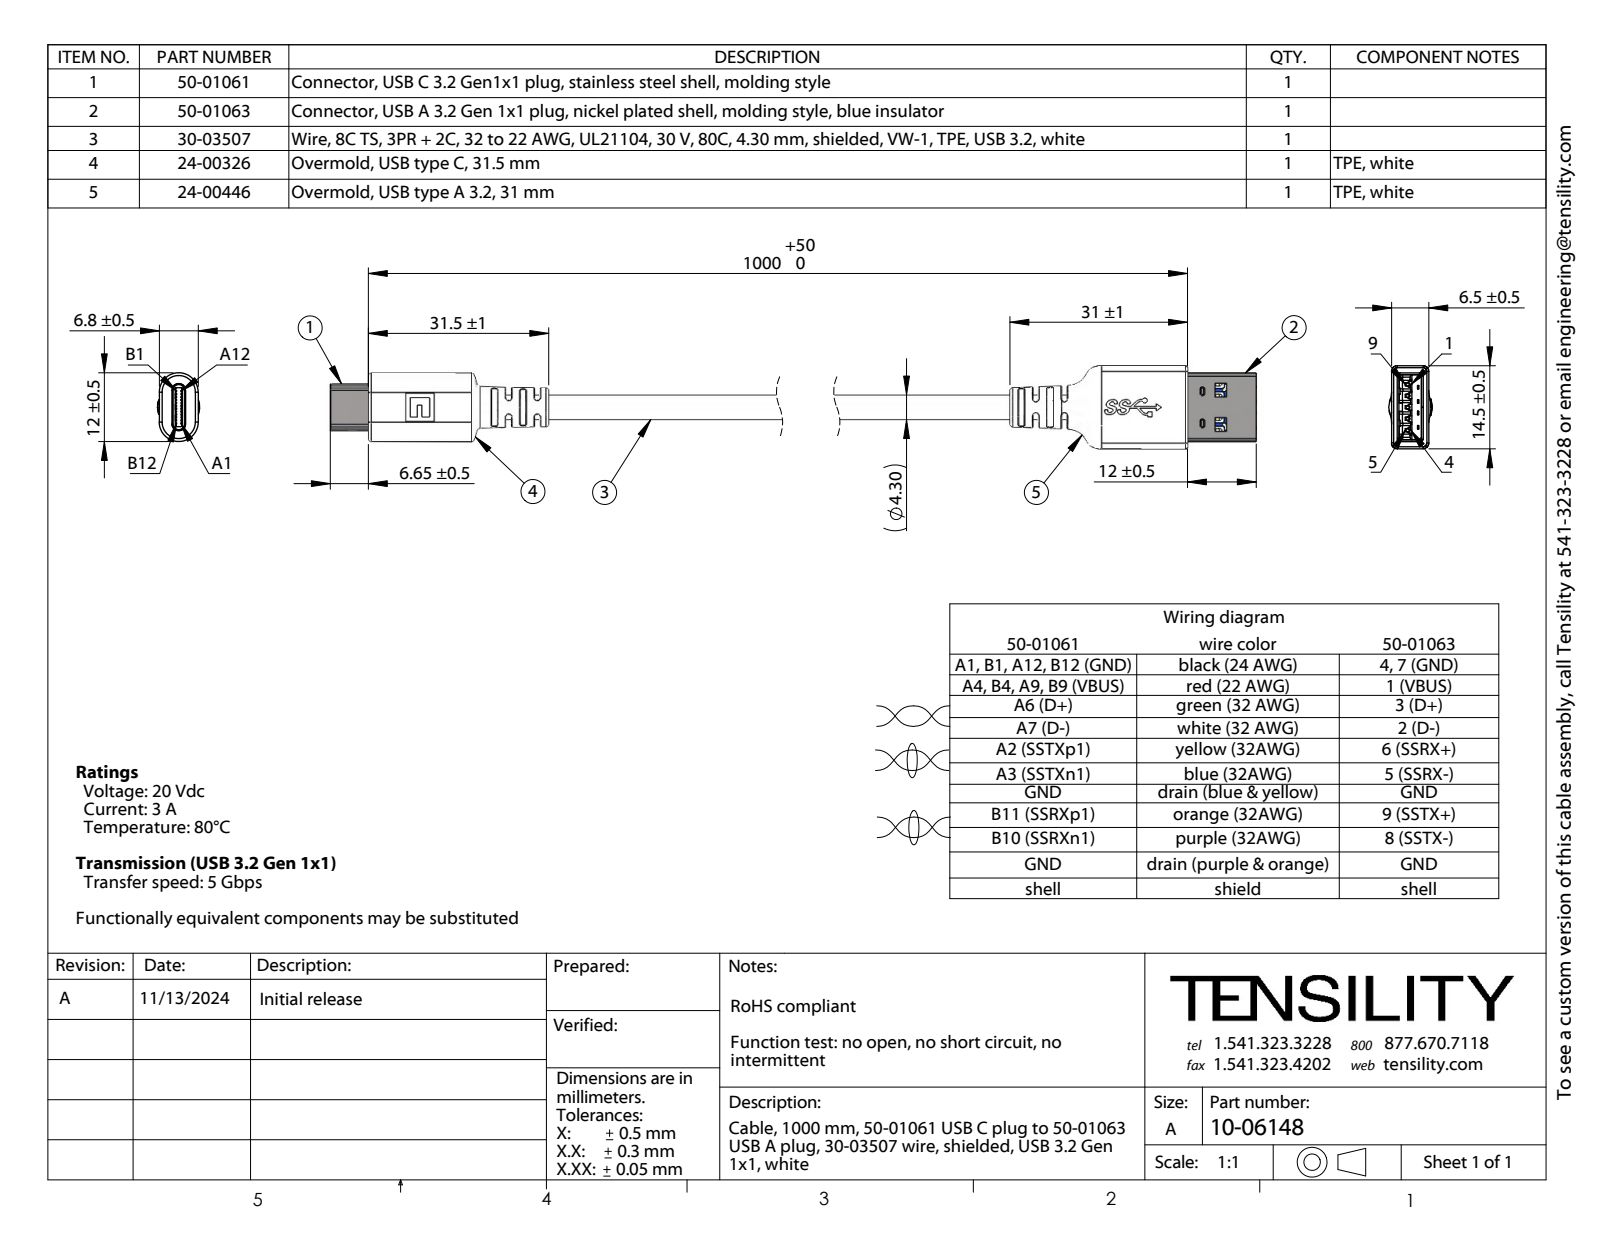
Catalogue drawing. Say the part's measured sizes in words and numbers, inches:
The part is named "50-01063_pin4; 10-06148; 50-01061_Hidden emarker; 50-01063_pin2 (+8 more)". Its 3-D file was written by "SolidWorks 2021 (CONFIG_CONTROL_DESIGN)". It is 131 solids with 2476 faces: 1293 planar, 809 cylindrical and 374 other. Overall it measures 8.313 by 0.571 by 0.297 inches. Its volume is 0.352 cubic inches and its surface area 46.19 square inches. Round holes: 1 of diameter 0.034, 1 of diameter 0.127, 1 of diameter 0.128, 1 of diameter 0.132. Round bosses or shafts: 4 of diameter 0.024, 2 of diameter 0.03, 2 of diameter 0.022, 2 of diameter 0.018, 1 of diameter 0.169, 1 of diameter 0.065, 1 of diameter 0.039, 1 of diameter 0.035. Partial cylindrical surfaces (rounded edges, fillets, slot ends): 30 of radius 0.004, 24 of radius 0.008, 20 of radius 0.02, 13 of radius 0.012, 10 of radius 0.016, 9 of radius 0.01, 7 of radius 0.014, 7 of radius 0.024. The main face-to-face distances are 0.167, 0.035, 0.035, 0.098, 0.014, 0.256, 0.122, 0.05, 0.039, 0.027. The hole center spacings are 0.013, 0.025, 0.036, 0.022, 0.028, 0.031, 0.037, 0.039.
